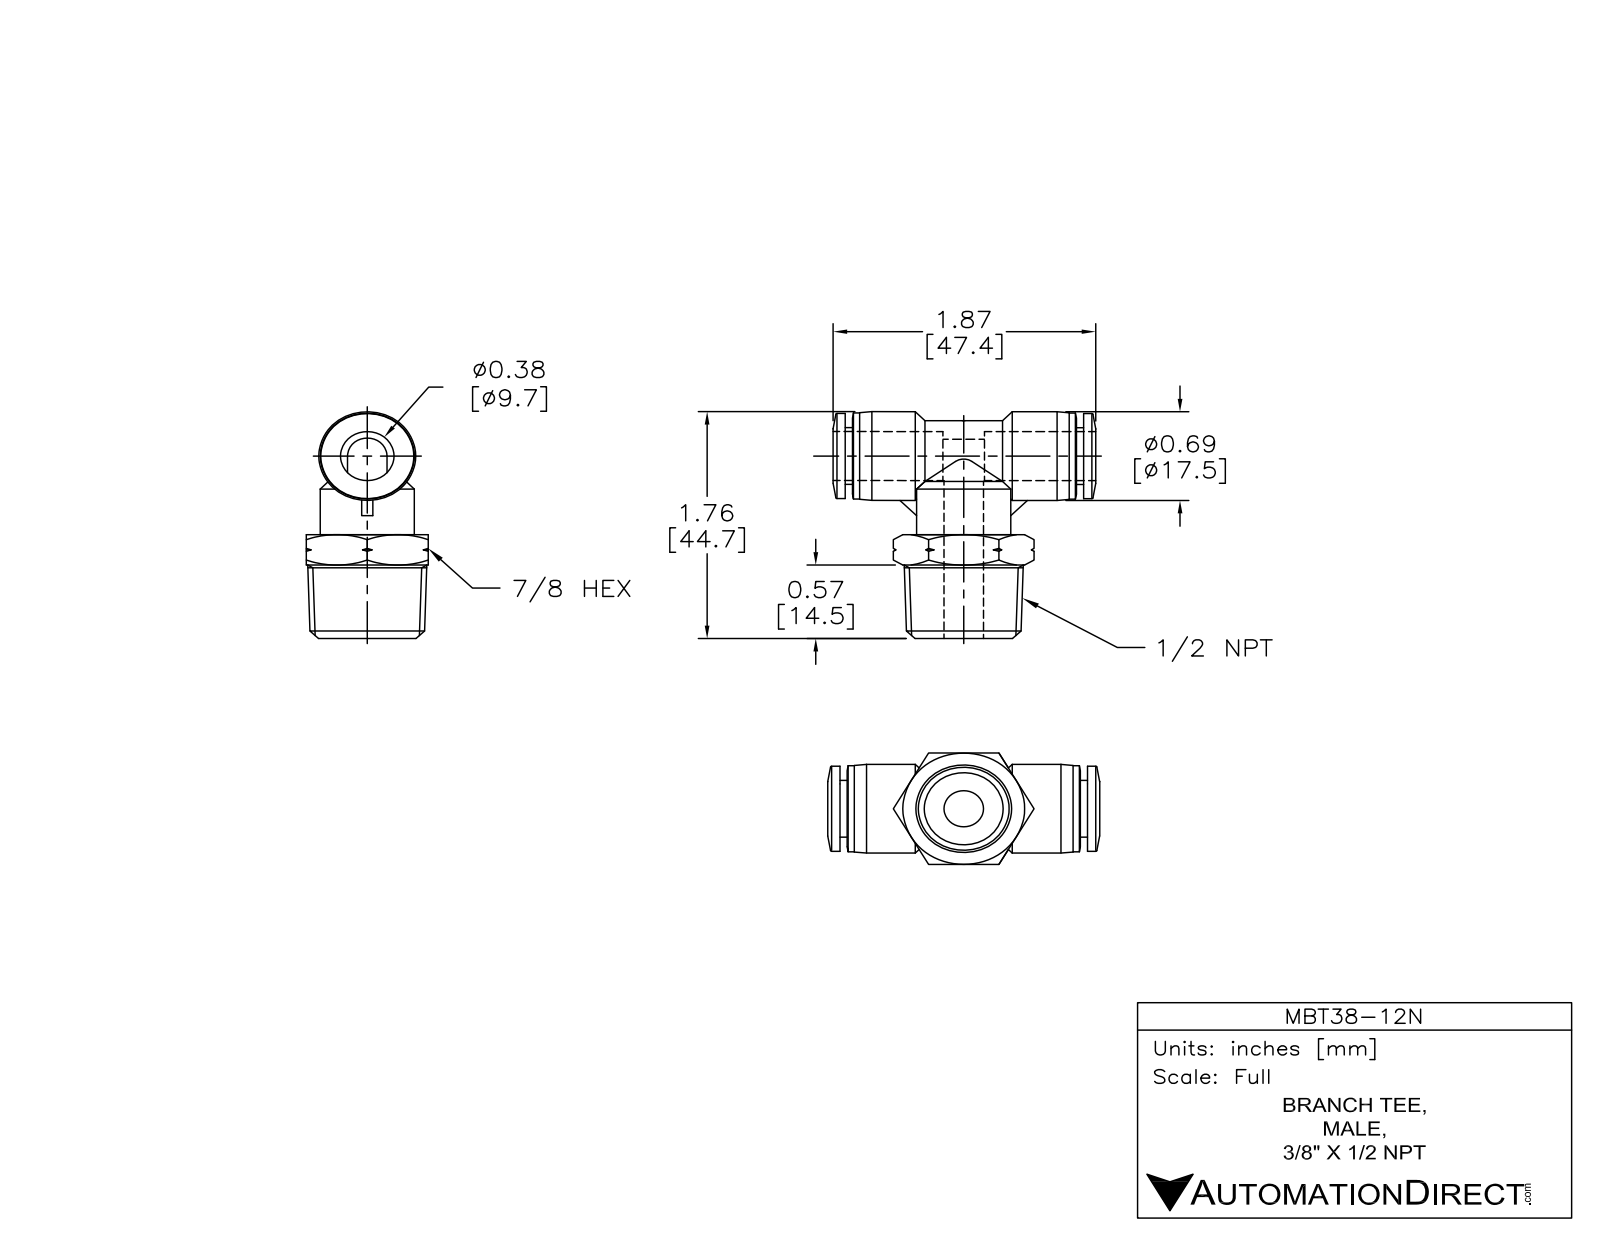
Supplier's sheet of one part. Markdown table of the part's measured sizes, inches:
| quantity | value |
| --- | --- |
| part name | MBT38-12N |
| STEP written by | SolidWorks 2015 (AUTOMOTIVE_DESIGN) |
| units | inches |
| bodies | 1 solid, 116 faces (23 planar, 31 cylindrical, 62 other) |
| overall size | 1.874 × 1.762 × 0.866 |
| volume | 0.892 in³ |
| surface area | 11.68 in² |
| round holes (diameter × count) | 0.276 × 2, 0.386 × 1 |
| round bosses / shafts (diameter × count) | 0.669 × 2, 0.689 × 1, 0.661 × 1, 0.441 × 1 |
| partial cylindrical surfaces (radius × count) | 0.276 × 2 |
| main face-to-face distances | 0.866, 0.051, 1.65, 0.807, 1.701, 1.598, 0.705, 0.996, 0.654, 0.945 |
